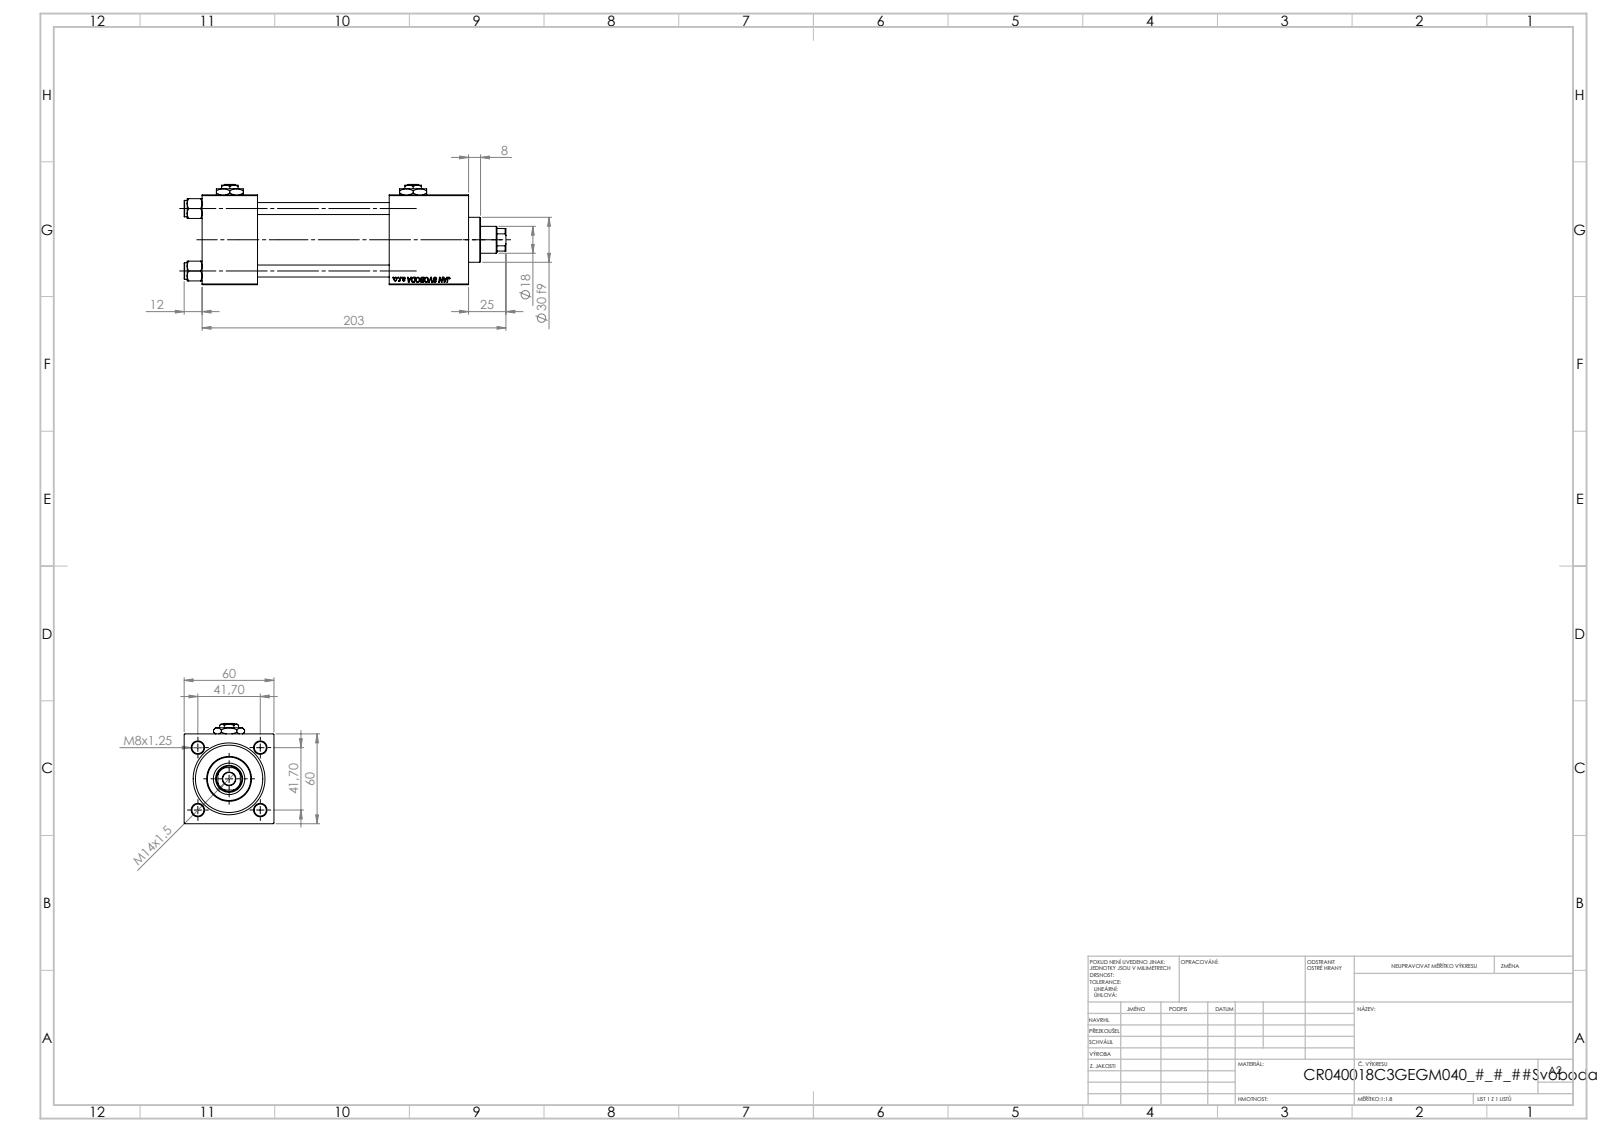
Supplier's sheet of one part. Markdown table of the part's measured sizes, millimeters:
| quantity | value |
| --- | --- |
| part name | V215CR_C_Body; V215CR_VCP_C; Zatka_pro_OIL_PORT; NUT_M5_C (+2 more) |
| STEP written by | SolidWorks 2019 (CONFIG_CONTROL_DESIGN) |
| units | millimeters |
| bodies | 13 solids, 1250 faces (574 planar, 98 cylindrical, 578 other) |
| overall size | 215 × 67 × 60 |
| volume | 424 665 mm³ |
| surface area | 121 153 mm² |
| round holes (diameter × count) | 8 × 4, 7 × 2, 16.66 × 2, 24 × 2, 8.5 × 1, 18 × 1, 21 × 1, 31 × 1, 40 × 1, 45 × 1 |
| round bosses / shafts (diameter × count) | 11 × 4, 46 × 1, 30 × 1 |
| partial cylindrical surfaces (radius × count) | 8.5 × 1 |
| main face-to-face distances | 60, 37, 178, 141, 53, 125, 88, 149.3, 112.3, 24.3 |
| hole center spacings | 29.49, 41.7, 58.97, 122.5 |
